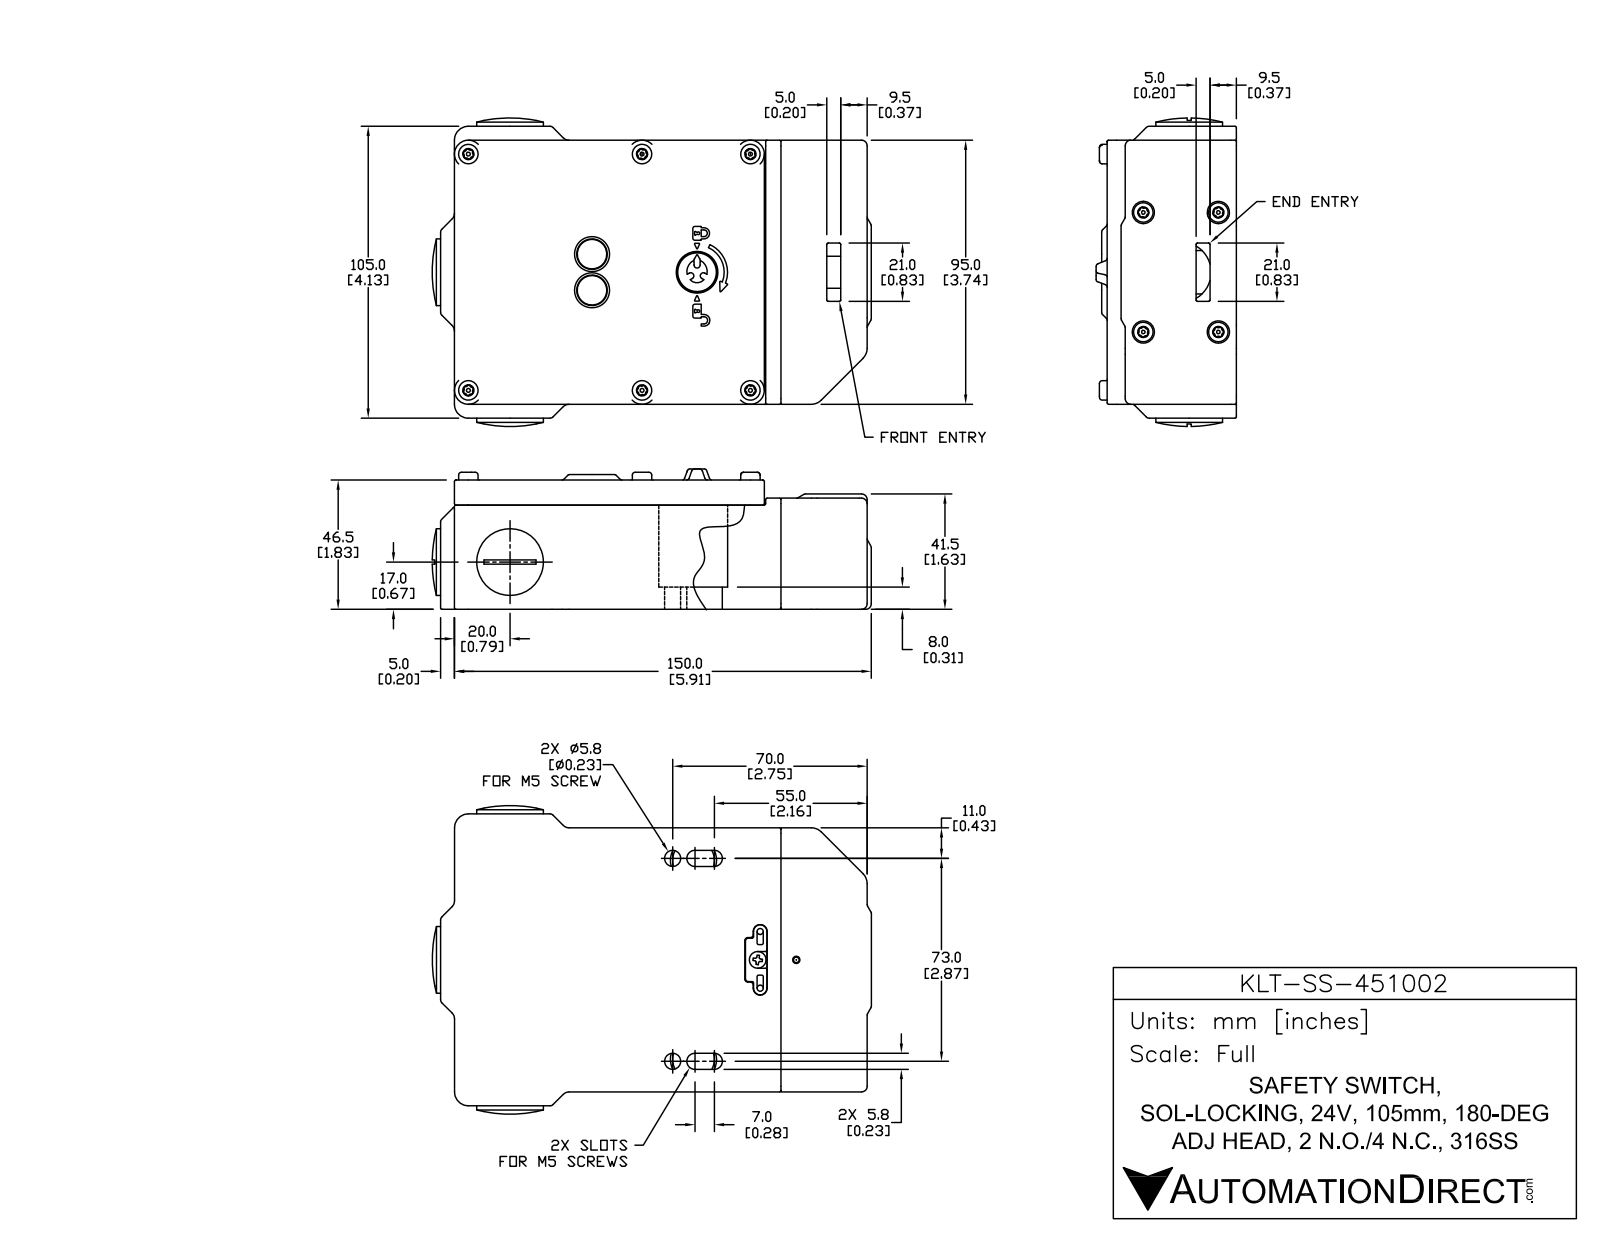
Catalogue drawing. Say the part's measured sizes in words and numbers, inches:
The part is named "KLT-SS-451002". Its 3-D file was written by "SolidWorks 2017 (AUTOMOTIVE_DESIGN)". It is 21 solids with 3390 faces: 741 planar, 1370 cylindrical and 1279 other. Overall it measures 6.22 by 4.37 by 1.988 inches. Its volume is 14 cubic inches and its surface area 209.2 square inches. Round holes: 10 of diameter 0.13, 10 of diameter 0.157, 8 of diameter 0.098, 6 of diameter 0.177, 6 of diameter 0.185, 4 of diameter 0.165, 4 of diameter 0.197, 4 of diameter 0.315, 3 of diameter 0.591, 2 of diameter 0.087, 2 of diameter 0.217, 2 of diameter 0.228. Round bosses or shafts: 10 of diameter 0.276, 10 of diameter 0.138, 6 of diameter 0.055, 5 of diameter 0.236, 4 of diameter 0.051, 3 of diameter 0.709, 2 of diameter 0.945, 2 of diameter 0.449. Partial cylindrical surfaces (rounded edges, fillets, slot ends): 451 of radius 0.02, 162 of radius 0.039, 54 of radius 0.012, 21 of radius 0.079, 14 of radius 0.006, 14 of radius 0.008, 10 of radius 0.197, 8 of radius 0.031. The main face-to-face distances are 0.118, 0.087, 1.831, 0.134, 1.744, 0.098, 0.138, 3.606, 0.256, 1.476. The hole center spacings are 1, 2.606, 1.648, 3.346, 0.187, 0.296, 0.383, 0.396.
